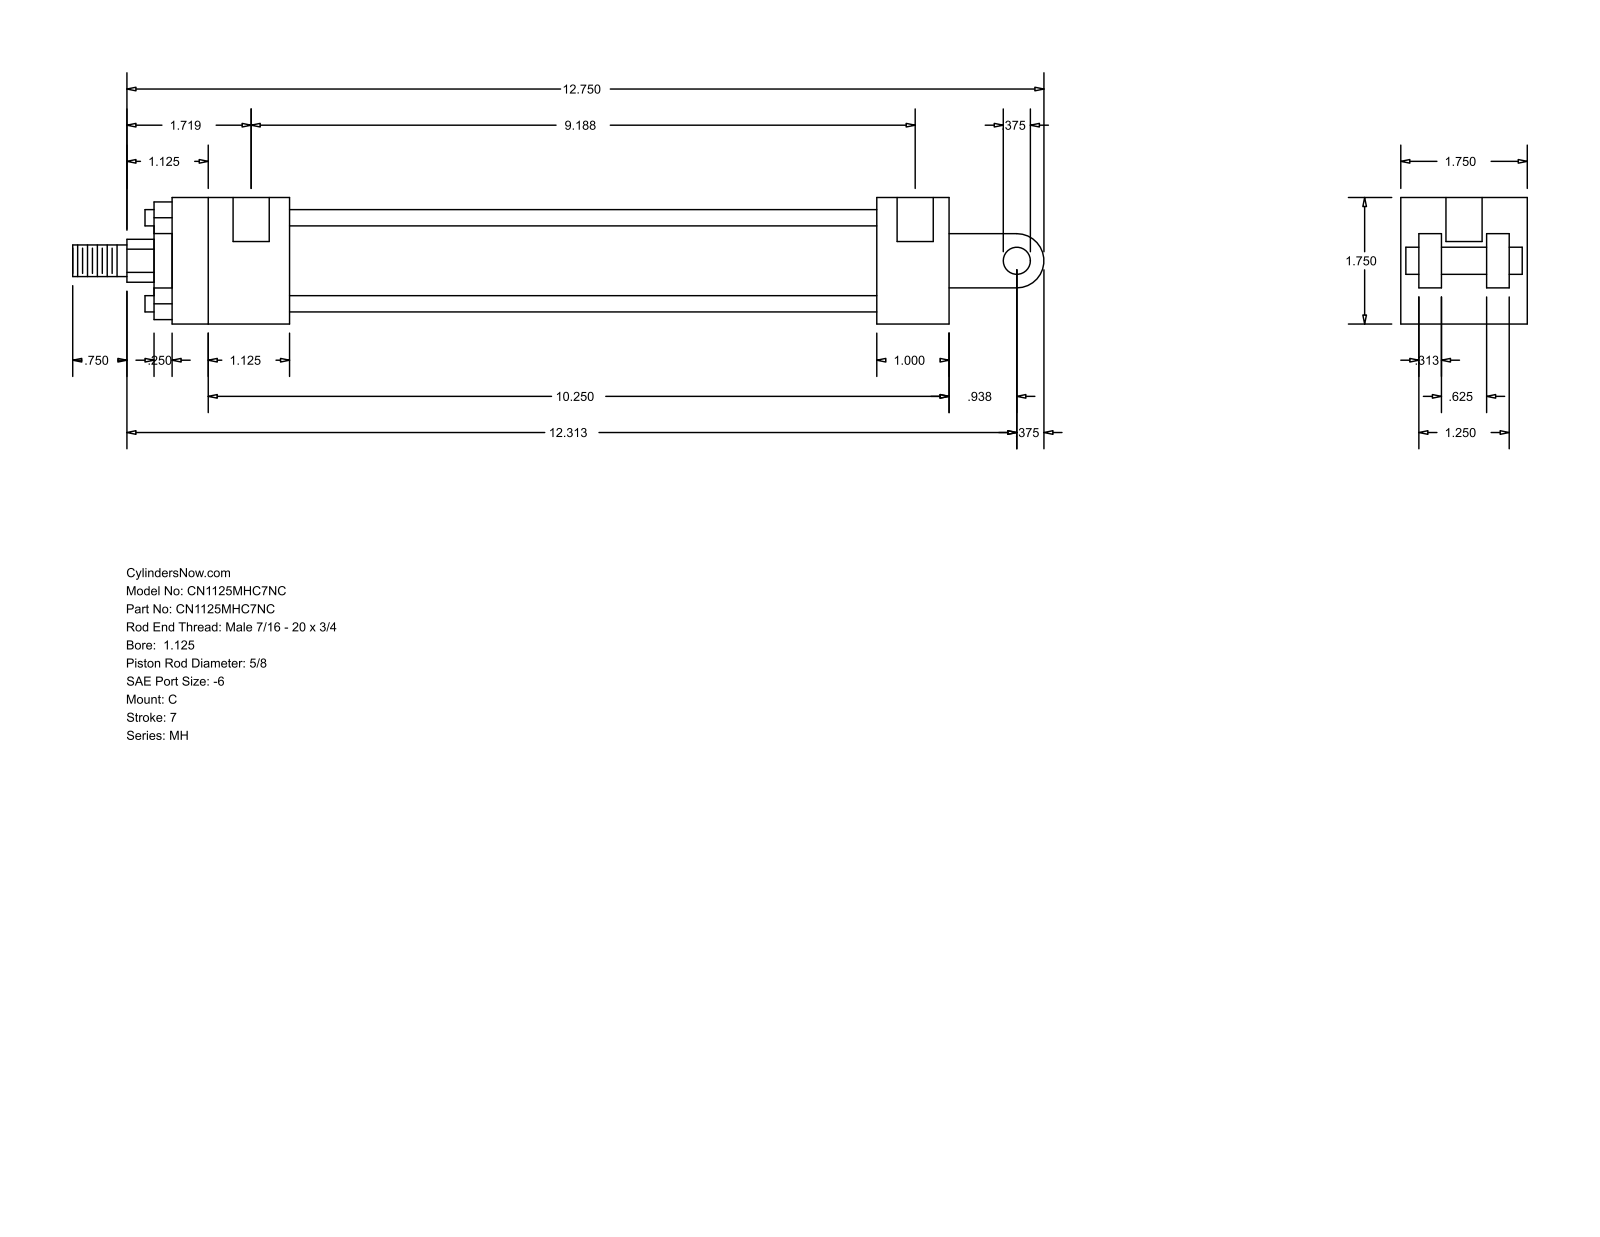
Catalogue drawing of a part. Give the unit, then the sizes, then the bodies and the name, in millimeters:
Units: millimetres
Overall size (bounding box): 341.31 × 44.45 × 44.45
Round holes (diameter × count): ⌀5.56 ×4, ⌀12.7 ×2
Round bosses / shafts (diameter × count): ⌀5.71 ×4, ⌀34.92 ×1, ⌀28.57 ×1, ⌀15.88 ×1, ⌀11.11 ×1, ⌀9.53 ×1
Partial cylindrical surfaces — rounded edges, fillets, slot ends (radius × count): R7.54 ×1, R9.53 ×1
Main face-to-face distances: 44.46, 6.35, 31.76, 14.29, 30.17, 38.11, 7.94, 23.82, 41.27, 12.7
Hole centre spacings: 230.19, 3.17, 233.36
Bodies: 0 solids, 99 faces (70 planar, 29 cylindrical, 0 other)
Part name (STEP PRODUCT): MH_C__0112_0.625
STEP written by: GSSL Pune (CONFIG_CONTROL_DESIGN)
